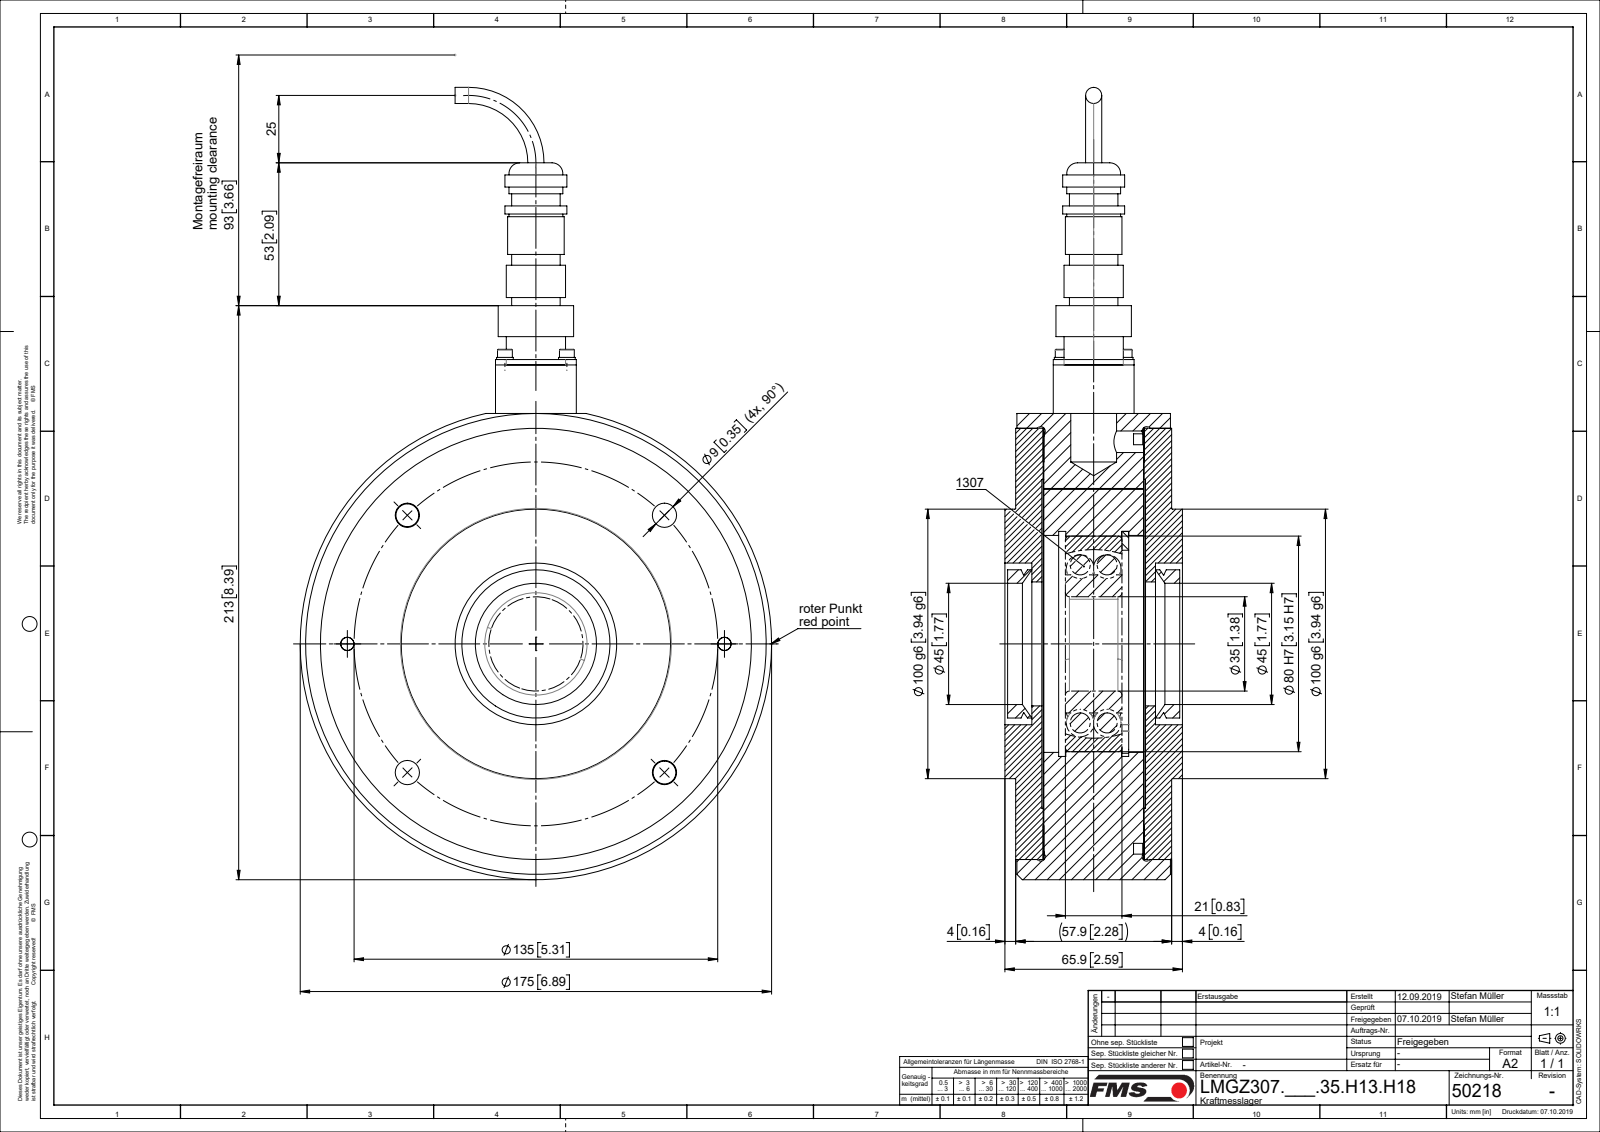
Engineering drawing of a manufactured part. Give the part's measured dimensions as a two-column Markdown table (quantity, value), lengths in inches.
| quantity | value |
| --- | --- |
| part name | L50218; L4857104; TEIL1; L48573 (+8 more) |
| STEP written by | Mechanical Desktop 2007 (CONFIG_CONTROL_DESIGN) |
| units | inches |
| bodies | 21 solids, 386 faces (89 planar, 235 cylindrical, 62 other) |
| overall size | 12.5 × 11.575 × 4.122 |
| volume | 79.21 in³ |
| surface area | 417.9 in² |
| round holes (diameter × count) | 0.102 × 4, 0.126 × 4, 0.134 × 4, 0.354 × 4, 0.197 × 2, 0.26 × 2, 0.433 × 2, 1.378 × 1, 1.732 × 1, 1.811 × 1, 2.362 × 1, 2.445 × 1 |
| round bosses / shafts (diameter × count) | 0.244 × 4, 0.217 × 4, 0.118 × 4, 0.098 × 4, 0.236 × 3, 0.394 × 2, 6.89 × 1, 6.299 × 1 |
| partial cylindrical surfaces (radius × count) | 0.157 × 4, 0.295 × 2 |
| main face-to-face distances | 1.467, 0.402, 0.411, 1.868, 1.878, 1.457, 1.496, 0.382, 1.898, 0.02 |
| hole center spacings | 0.906, 2.074, 2.657, 3.758, 5.002, 1.281, 2.756, 5.315 |
